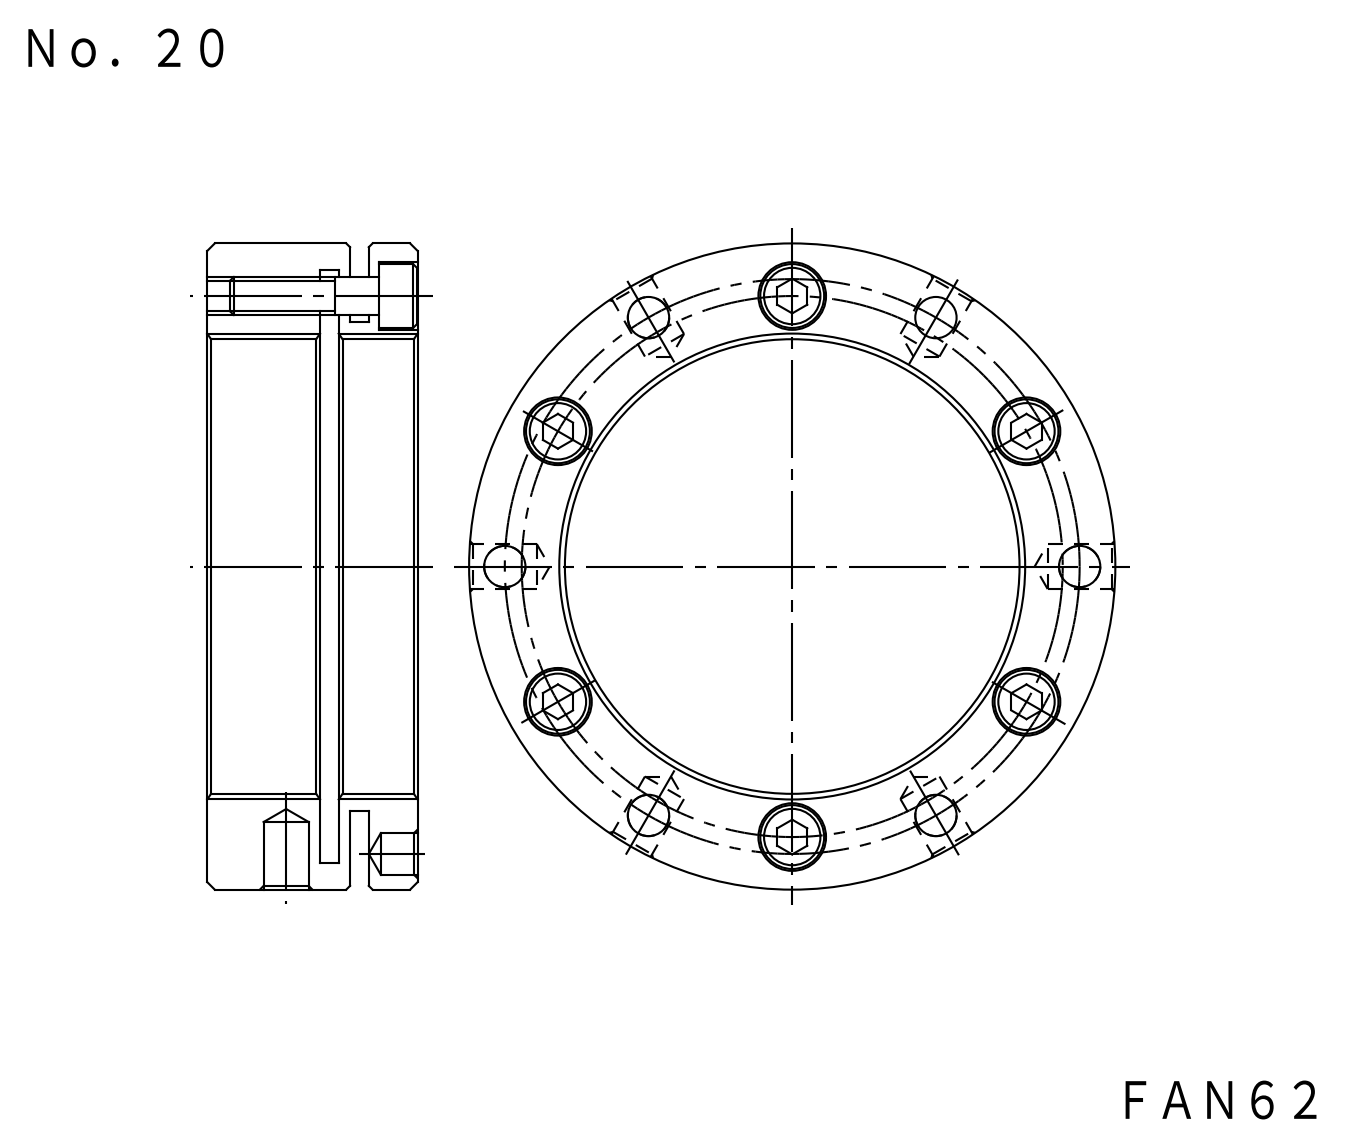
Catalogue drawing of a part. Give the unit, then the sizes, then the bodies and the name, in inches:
Units: inches
Overall size (bounding box): 3.386 × 3.386 × 1.102
Round holes (diameter × count): ⌀0.163 ×6, ⌀0.209 ×6, ⌀0.217 ×6, ⌀0.354 ×6, ⌀0.236 ×3, ⌀2.441 ×1, ⌀3.15 ×1
Round bosses / shafts (diameter × count): ⌀0.335 ×6, ⌀0.197 ×6, ⌀3.386 ×1, ⌀2.677 ×1
Main face-to-face distances: 0.098, 0.157, 0.551, 1.102, 0.709, 0.394, 0.807, 0.295, 0.256, 0.65
Hole centre spacings: 1.457, 2.095, 0.768, 1.506, 2.862, 2.523, 1.506, 2.609
Volume: 4.019 in³ · Surface area: 51.94 in²
Bodies: 7 solids, 204 faces (72 planar, 108 cylindrical, 24 other)
Part name (STEP PRODUCT): FKD FAN62; M5X20_default
STEP written by: SolidWorks 2012 (CONFIG_CONTROL_DESIGN)
